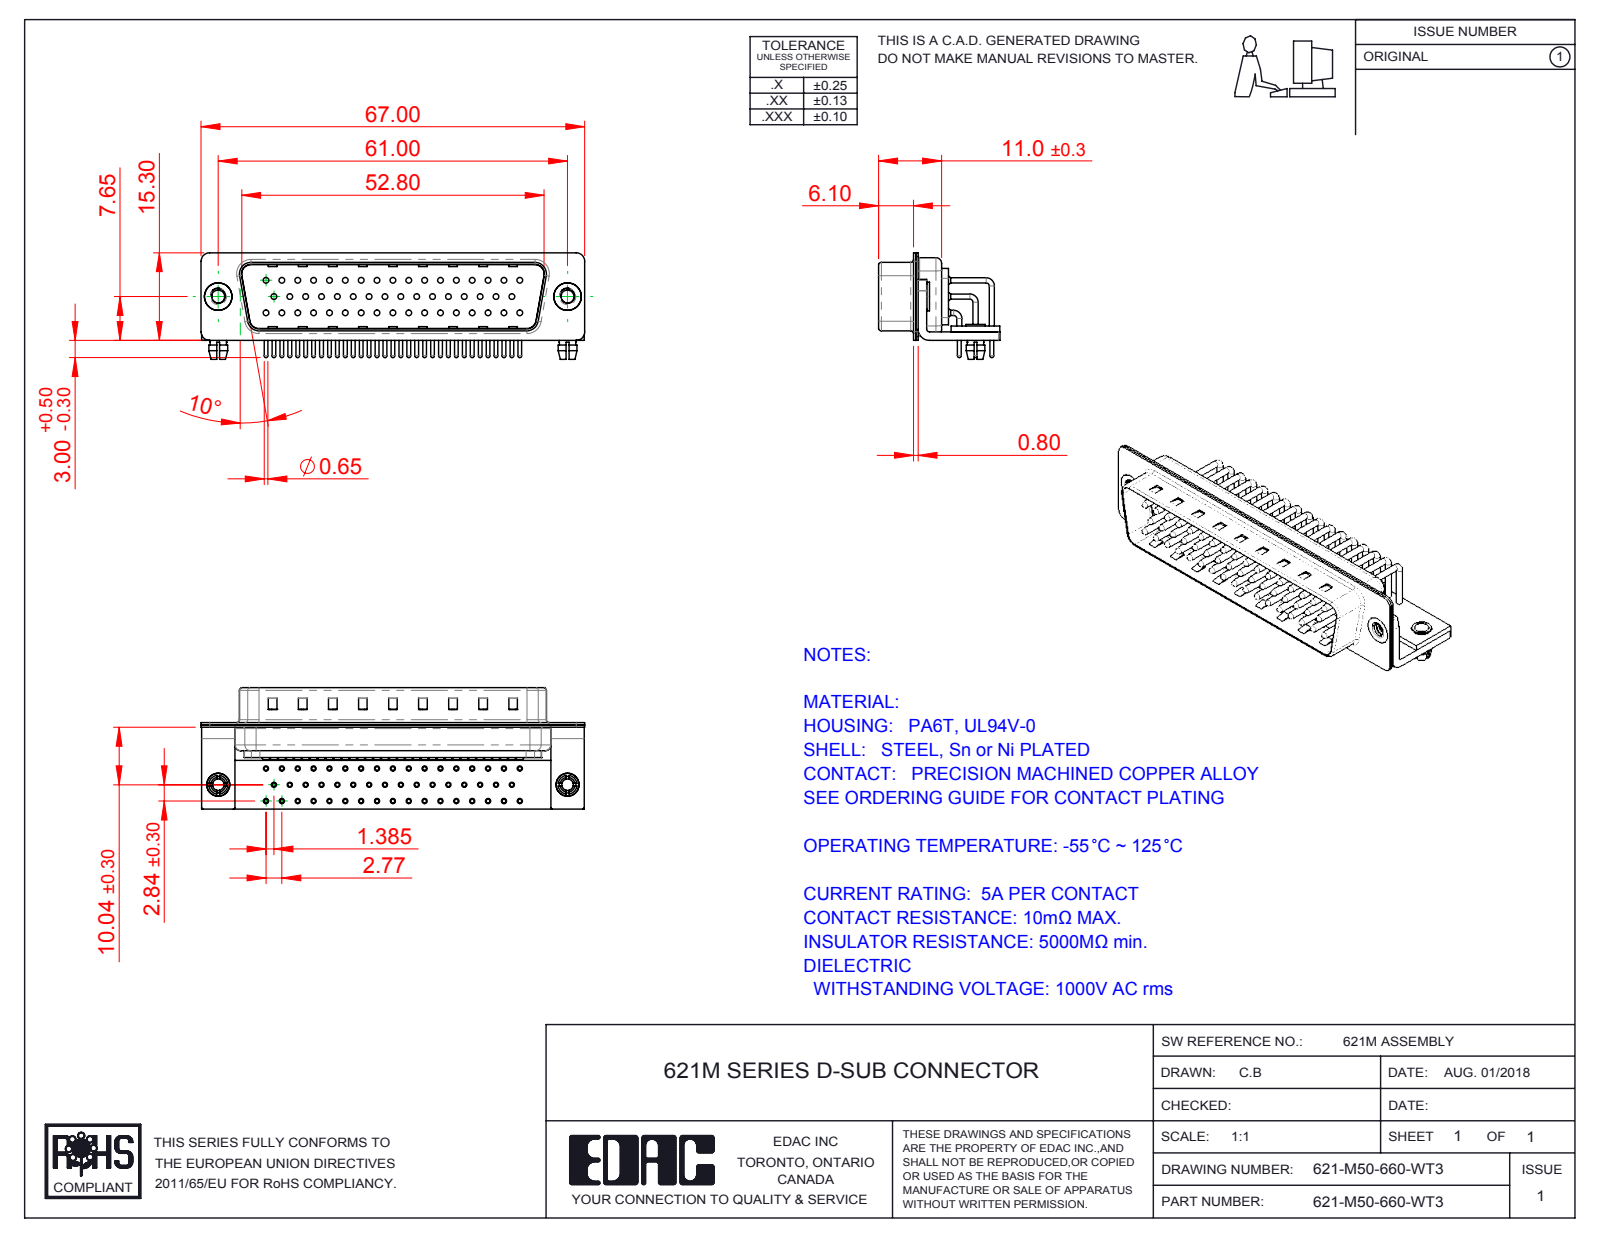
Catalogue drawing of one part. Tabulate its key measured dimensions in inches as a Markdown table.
| quantity | value |
| --- | --- |
| part name | 621M 4-40 Threaded Rivet_Stabilizer; 621M Contact Row 2_50 Contacts; 621-M50-660-WT3; 621M Housing_50 Contacts (+7 more) |
| STEP written by | SolidWorks 2016 (CONFIG_CONTROL_DESIGN) |
| units | inches |
| bodies | 60 solids, 6154 faces (3477 planar, 2095 cylindrical, 582 other) |
| overall size | 2.638 × 0.835 × 0.732 |
| volume | 0.353 in³ |
| surface area | 22.94 in² |
| round holes (diameter × count) | 0.079 × 52, 0.035 × 50, 0.039 × 50, 0.067 × 50, 0.089 × 2, 0.098 × 2, 0.126 × 2, 0.157 × 2, 0.189 × 2 |
| round bosses / shafts (diameter × count) | 0.035 × 58, 0.059 × 50, 0.026 × 50, 0.197 × 2, 0.193 × 2, 0.157 × 2, 0.134 × 2, 0.13 × 2 |
| partial cylindrical surfaces (radius × count) | 0.04 × 50, 0.01 × 16, 0.059 × 16, 0.079 × 13, 0.02 × 9, 0.063 × 8, 0.024 × 4, 0.026 × 4 |
| main face-to-face distances | 0.016, 0.039, 0.455, 0.033, 0.059, 0.224, 0.017, 0.47, 0.24, 0.461 |
| hole center spacings | 0.109, 0.124, 0.218, 0.327, 0.436, 0.545, 0.654, 0.763 |
